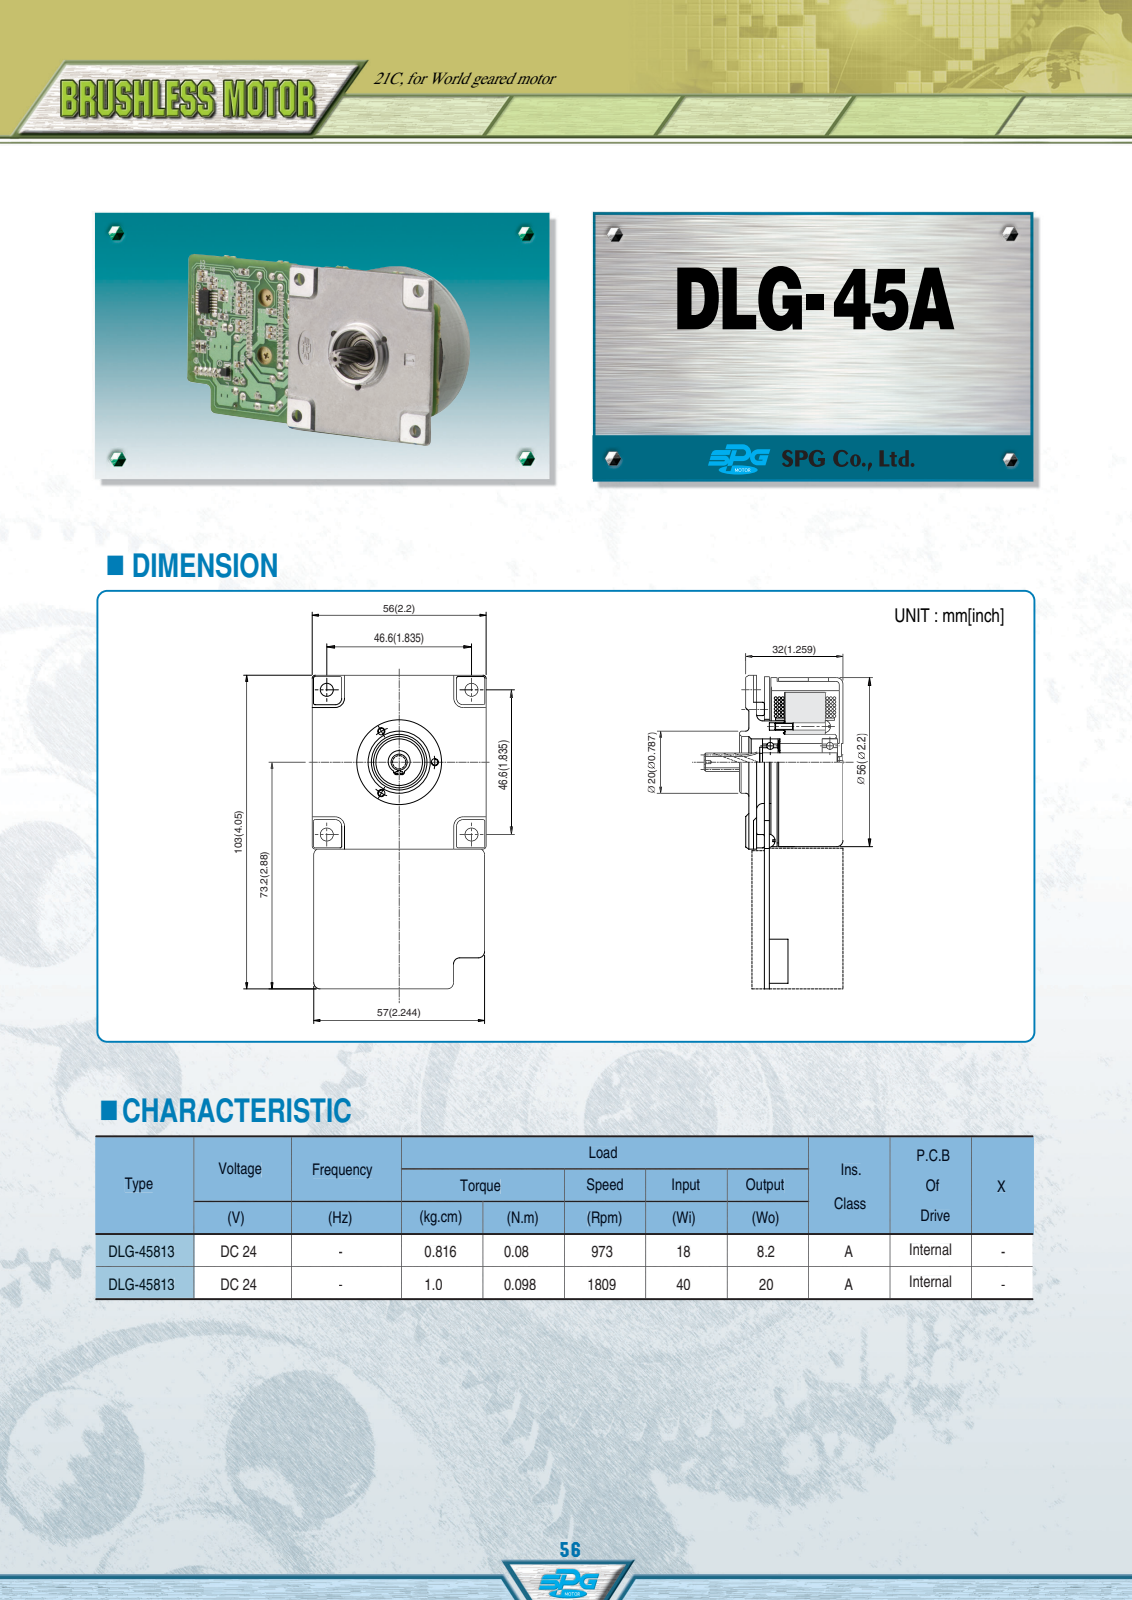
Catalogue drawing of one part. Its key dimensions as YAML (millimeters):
part_name: "부품15"
step_written_by: "Autodesk Inventor 2011 (AUTOMOTIVE_DESIGN)"
units: millimeters
bodies: {solids: 1, faces: 309, planar: 151, cylindrical: 73, other: 85}
overall_size: [104.2, 56, 52.8]
volume: 58412
surface_area: 29903
round_holes:
  - {diameter: 2.3, count: 7}
  - {diameter: 2.6, count: 4}
  - {diameter: 4.5, count: 4}
  - {diameter: 5.17, count: 1}
  - {diameter: 12, count: 1}
  - {diameter: 15, count: 1}
  - {diameter: 16.5, count: 1}
  - {diameter: 26.8, count: 1}
  - {diameter: 27.3, count: 1}
  - {diameter: 48.4, count: 1}
round_bosses_or_shafts:
  - {diameter: 2.24, count: 4}
  - {diameter: 54.4, count: 1}
  - {diameter: 52, count: 1}
  - {diameter: 26.6, count: 1}
  - {diameter: 20, count: 1}
  - {diameter: 19.8, count: 1}
  - {diameter: 7.07, count: 1}
  - {diameter: 5.9, count: 1}
partial_cylinders:
  - {radius: 2, count: 8}
  - {radius: 1, count: 6}
  - {radius: 2.4, count: 4}
  - {radius: 4.5, count: 4}
  - {radius: 5, count: 4}
  - {radius: 0.32, count: 2}
  - {radius: 0.56, count: 2}
  - {radius: 0.7, count: 2}
face_to_face_distances: [1.6, 2.5, 6.6, 5, 4.1, 25.3, 30.3, 27.8, 23.7, 17.3]
hole_center_spacings: [7.18, 30.15, 32.95, 39.75, 46.6, 49.09, 62.75, 11.5]
